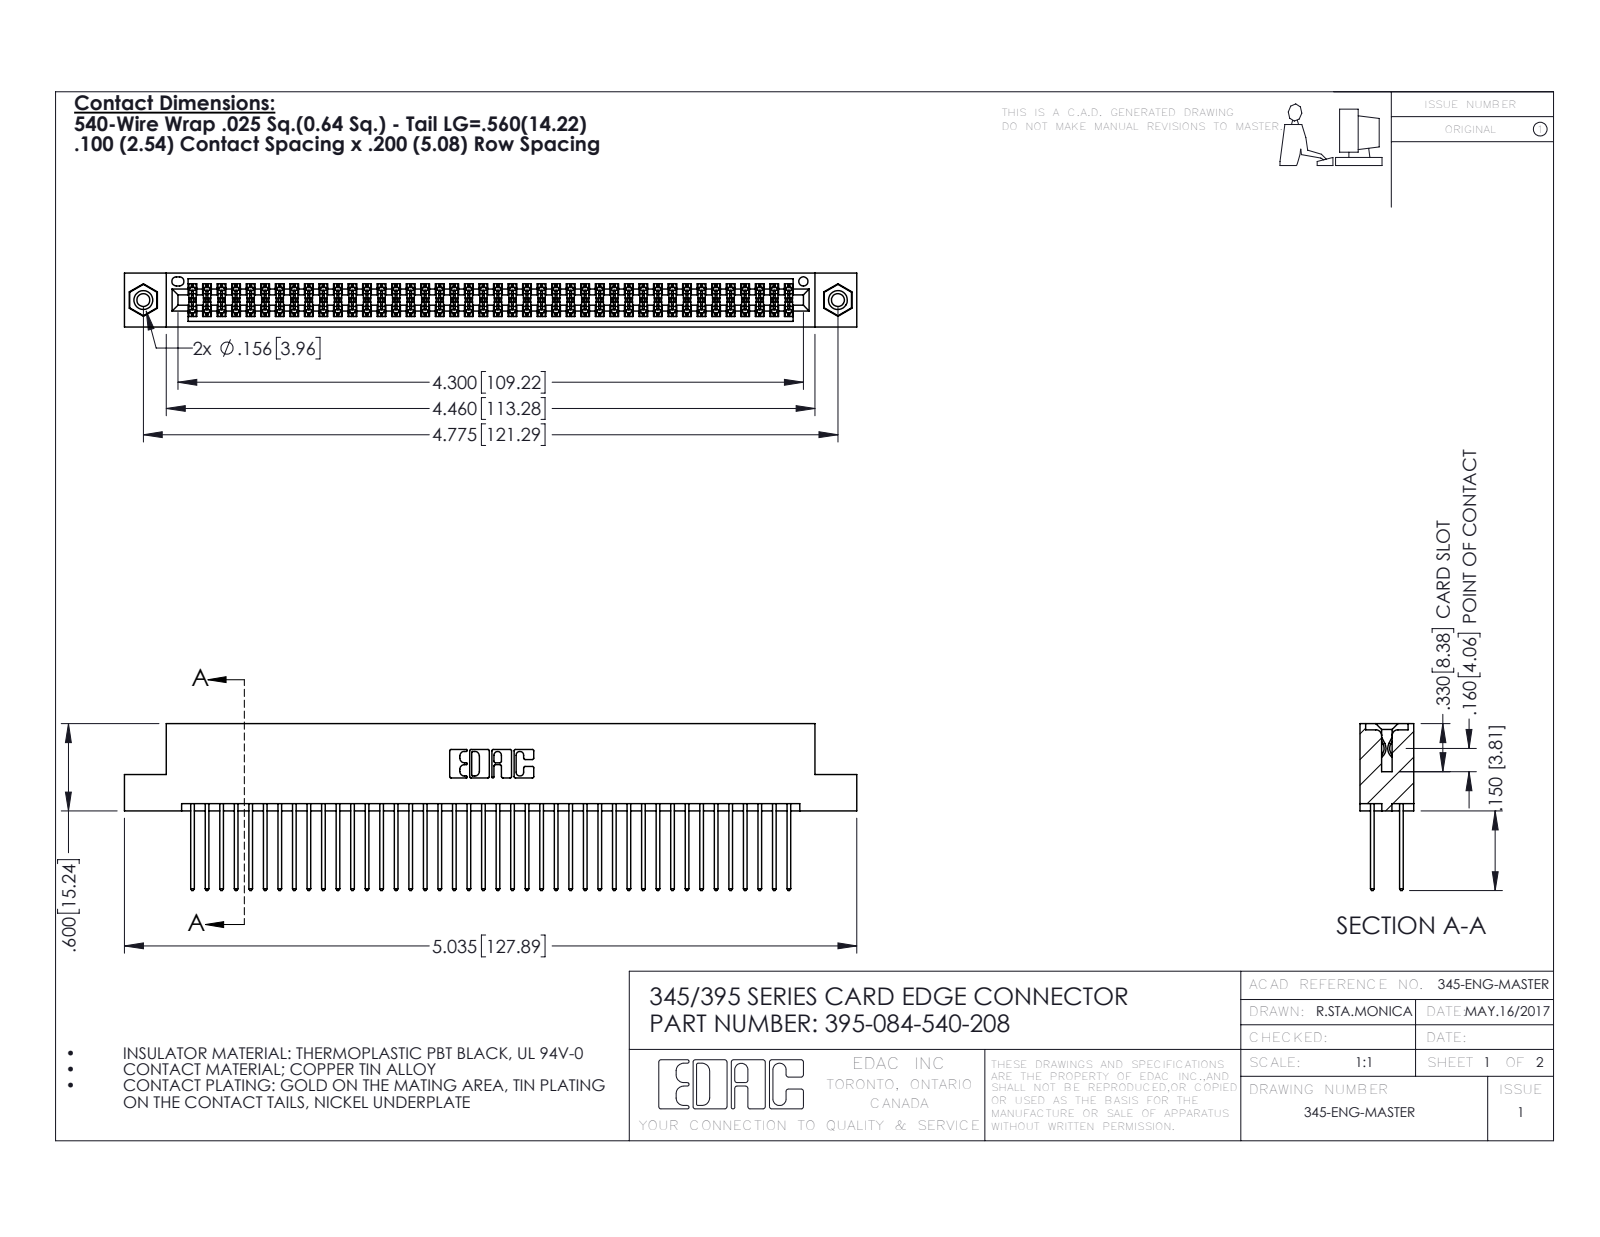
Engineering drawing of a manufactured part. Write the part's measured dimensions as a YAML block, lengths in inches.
part_name: "345-292-001_345-293-140; 395-084-540-208; 345-250-001_345-250-003-102; 345 Part_Flush Mounting Lugs - 0.156 Dia-TI"
step_written_by: "SolidWorks 2016 (CONFIG_CONTROL_DESIGN)"
units: inches
bodies: {solids: 87, faces: 4386, planar: 2884, cylindrical: 1486, other: 16}
overall_size: [5.035, 1.147, 0.37]
volume: 0.777
surface_area: 31.49
round_holes:
  - {diameter: 0.089, count: 2}
  - {diameter: 0.125, count: 2}
  - {diameter: 0.156, count: 2}
  - {diameter: 0.064, count: 1}
round_bosses_or_shafts:
  - {diameter: 0.155, count: 2}
partial_cylinders:
  - {radius: 0.006, count: 126}
  - {radius: 0.01, count: 84}
  - {radius: 0.01, count: 22}
  - {radius: 0.007, count: 6}
  - {radius: 0.031, count: 6}
  - {radius: 0.026, count: 3}
  - {radius: 0.014, count: 2}
  - {radius: 0.019, count: 2}
face_to_face_distances: [0.072, 0.298, 0.2, 0.098, 0.272, 0.025, 0.37, 0.225, 0.175, 0.149]
hole_center_spacings: [0.27, 4.539, 4.775]
